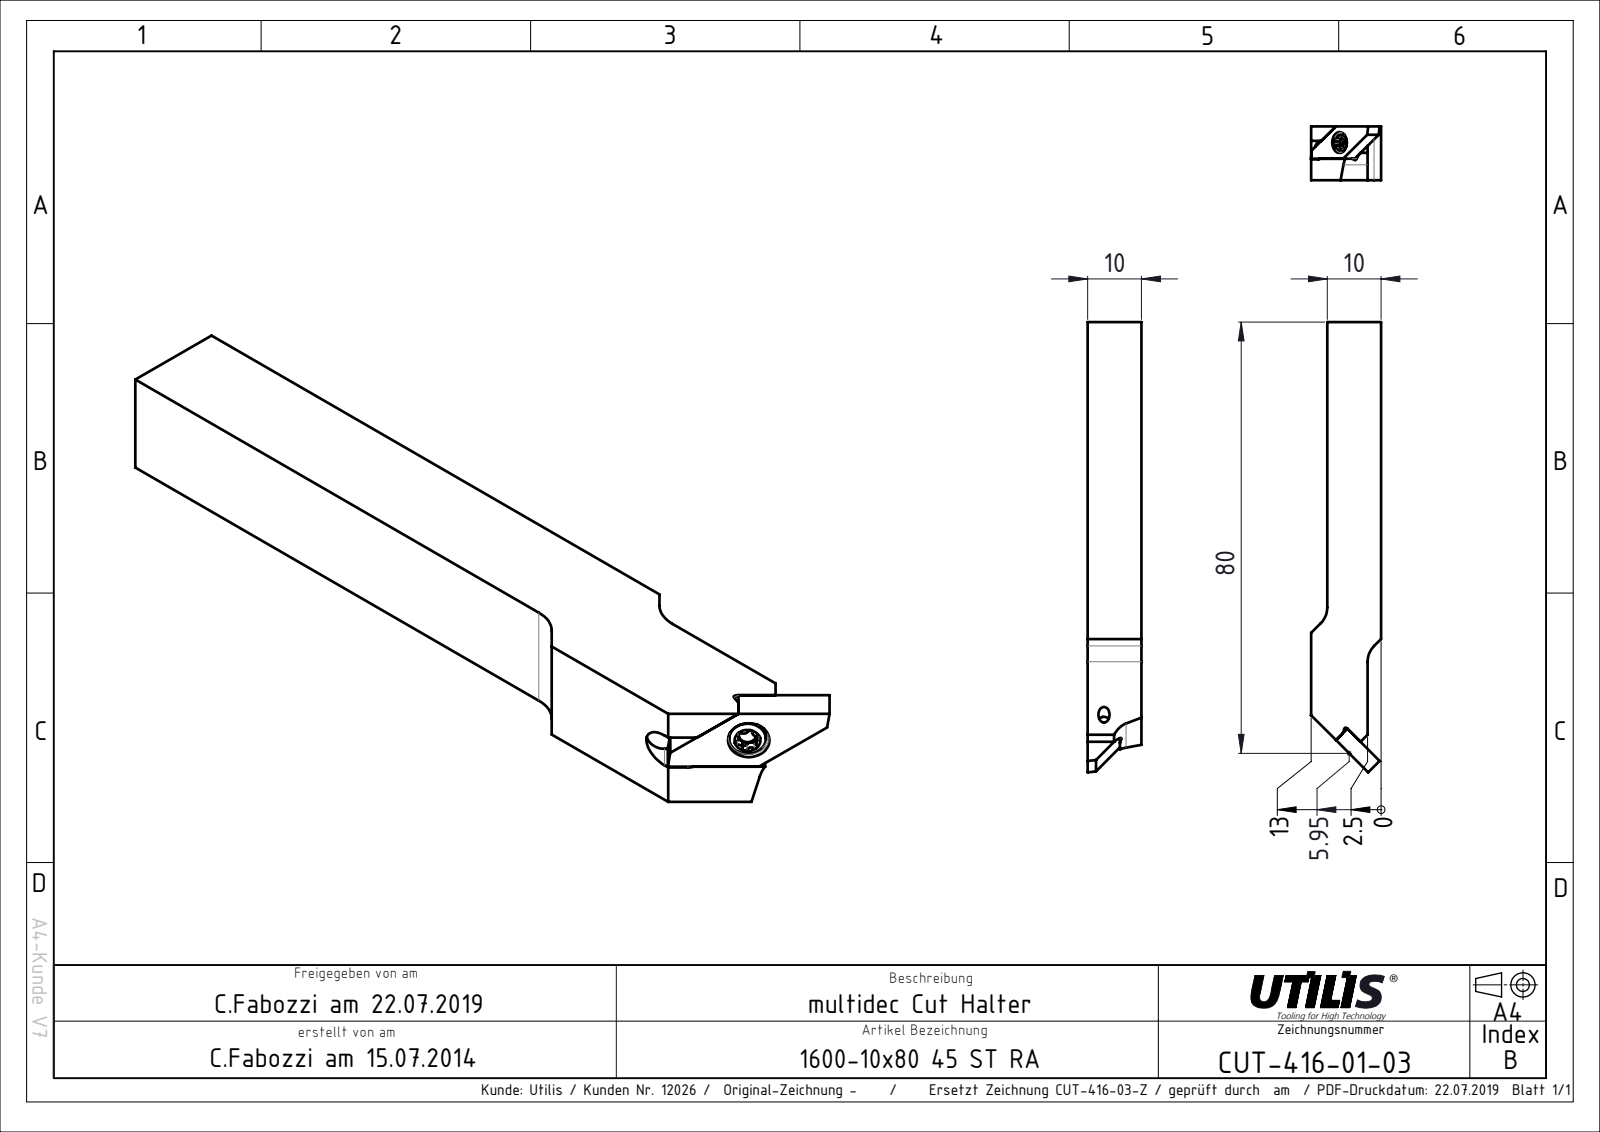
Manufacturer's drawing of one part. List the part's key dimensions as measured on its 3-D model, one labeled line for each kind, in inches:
Part name (STEP PRODUCT): CUT-Vorlage 1600_1600 Vorlage; CUT-416_03; CUT-416-01-03
STEP written by: SolidWorks 2020 (AUTOMOTIVE_DESIGN)
Units: inches
Bodies: 2 solids, 42 faces (27 planar, 8 cylindrical, 7 other)
Overall size (bounding box): 3.289 × 0.513 × 0.394
Volume: 0.48 in³ · Surface area: 5.565 in²
Round holes (diameter × count): ⌀0.114 ×1, ⌀0.122 ×1
Partial cylindrical surfaces — rounded edges, fillets, slot ends (radius × count): R0.161 ×3, R0.02 ×1, R0.061 ×1, R0.067 ×1
Main face-to-face distances: 0.394, 0.118, 0.512, 0.098, 0.295, 0.413, 0.236, 0.157, 0.237, 0.818
